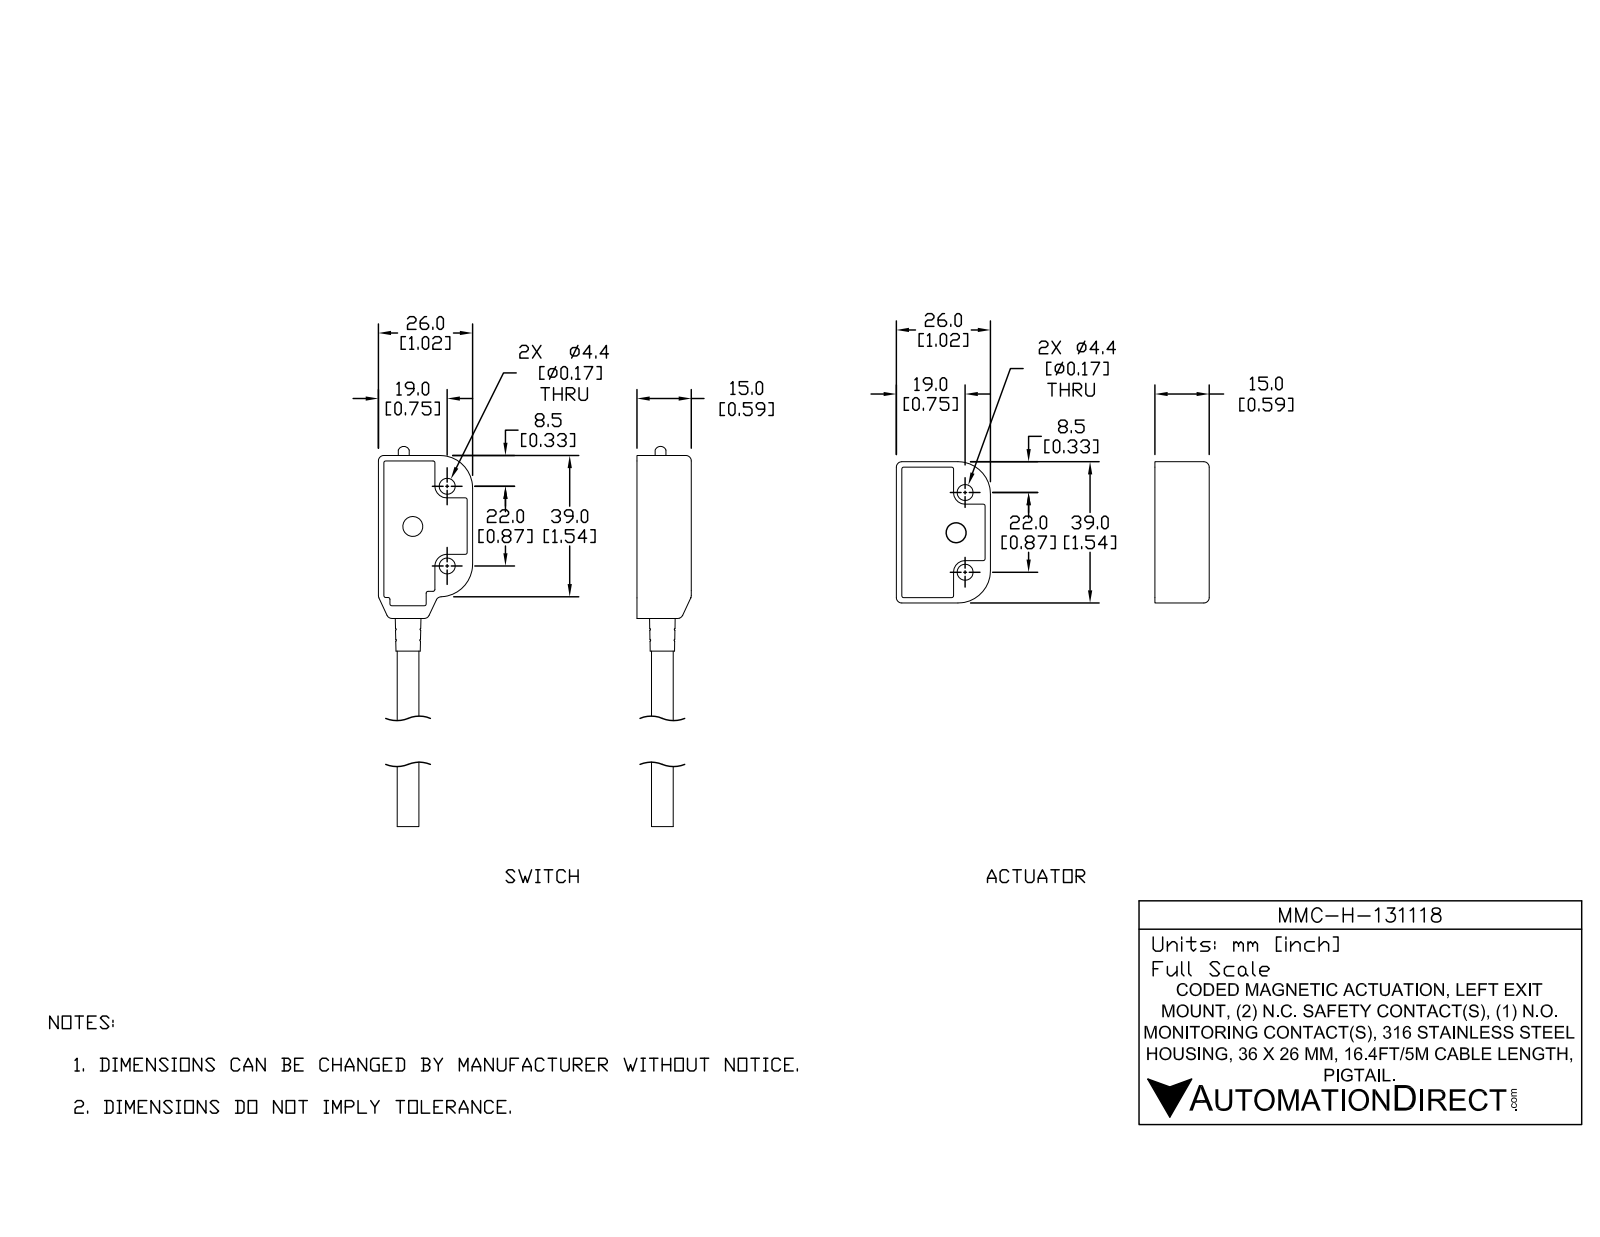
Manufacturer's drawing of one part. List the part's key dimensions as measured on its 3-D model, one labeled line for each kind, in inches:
Part name (STEP PRODUCT): MMC-H-131118; MMC-H-131118_2; MMC-H-131118_1
STEP written by: SolidWorks 2017 (AUTOMOTIVE_DESIGN)
Units: inches
Bodies: 9 solids, 603 faces (178 planar, 234 cylindrical, 191 other)
Overall size (bounding box): 7.902 × 2.087 × 0.591
Volume: 1.233 in³ · Surface area: 31 in²
Round holes (diameter × count): ⌀0.173 ×4, ⌀0.197 ×2, ⌀0.118 ×1, ⌀0.232 ×1, ⌀0.283 ×1
Round bosses / shafts (diameter × count): ⌀0.079 ×2, ⌀0.031 ×2, ⌀0.339 ×1, ⌀0.299 ×1, ⌀0.28 ×1, ⌀0.236 ×1, ⌀0.157 ×1
Partial cylindrical surfaces — rounded edges, fillets, slot ends (radius × count): R0.02 ×83, R0.012 ×26, R0.059 ×15, R0.008 ×8, R0.157 ×6, R0.126 ×4, R0.13 ×4, R0.181 ×4
Main face-to-face distances: 0.059, 0.575, 0.516, 0.098, 0.461, 0.52, 0.055, 0.591, 0.531, 0.965
Hole centre spacings: 0.572, 0.866, 1.239, 1.535, 1.763, 0.076, 0.44, 0.448
